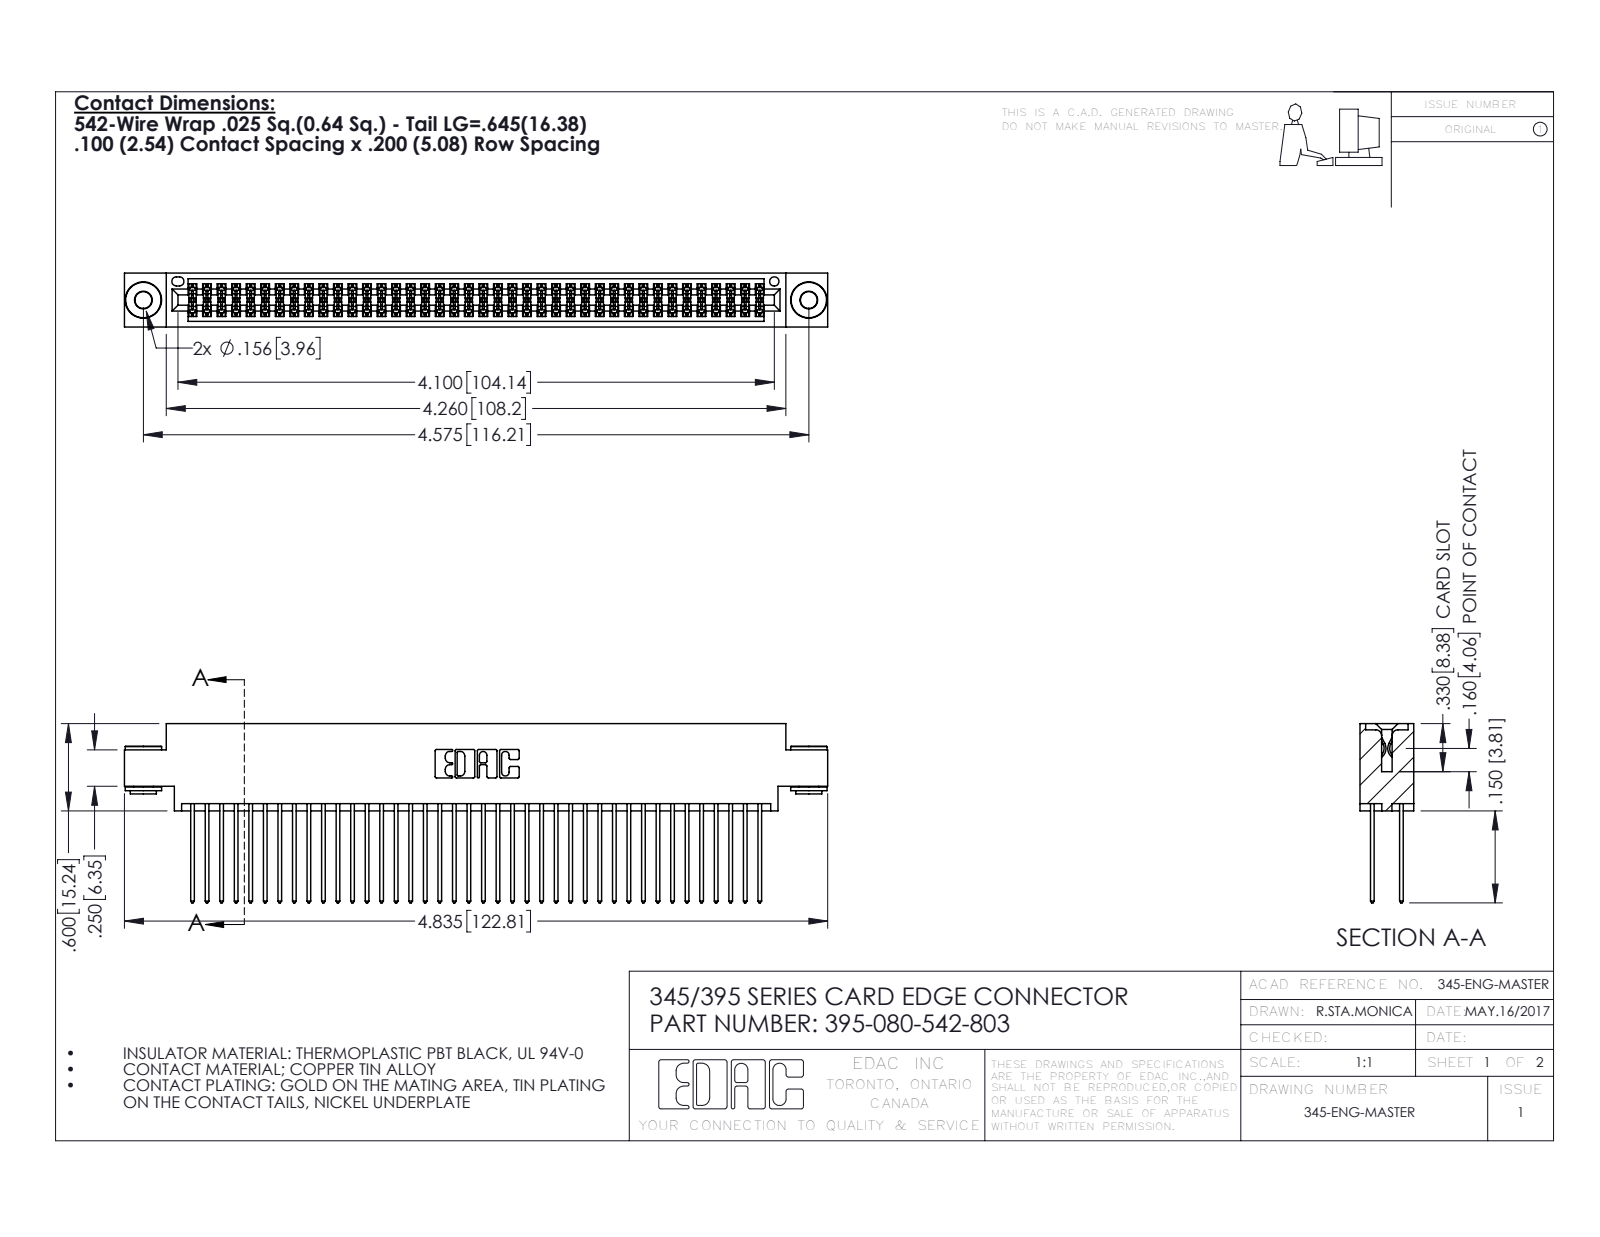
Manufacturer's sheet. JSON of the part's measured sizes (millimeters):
{"part_name": "345 Part_0.170 Offset - 0.156 Dia-TH; 345-292-001_345-293-142; 395-080-542-803; 345-250-002_345-250-002-102", "step_written_by": "SolidWorks 2016 (CONFIG_CONTROL_DESIGN)", "units": "millimeters", "bodies": {"solids": 83, "faces": 4168, "planar": 2734, "cylindrical": 1426, "other": 8}, "overall_size": [122.8, 31.3, 9.4], "volume_mm3": 12200, "surface_area_mm2": 20070, "round_holes": [[2.9, 2], [4, 2], [1.6, 1]], "round_bosses_or_shafts": [[6.4, 2], [4.6, 2], [3.5, 2]], "partial_cylinders_radius": [[0.2, 120], [0.3, 80], [0.3, 22], [0.2, 6], [0.8, 6], [0.7, 3], [0.4, 2], [0.5, 2]], "face_to_face_distances": [1.8, 7.6, 5.1, 2.5, 6.9, 0.6, 9.4, 5.7, 4.4, 3.8], "hole_center_spacings": [6.9, 110.2, 116.2]}
